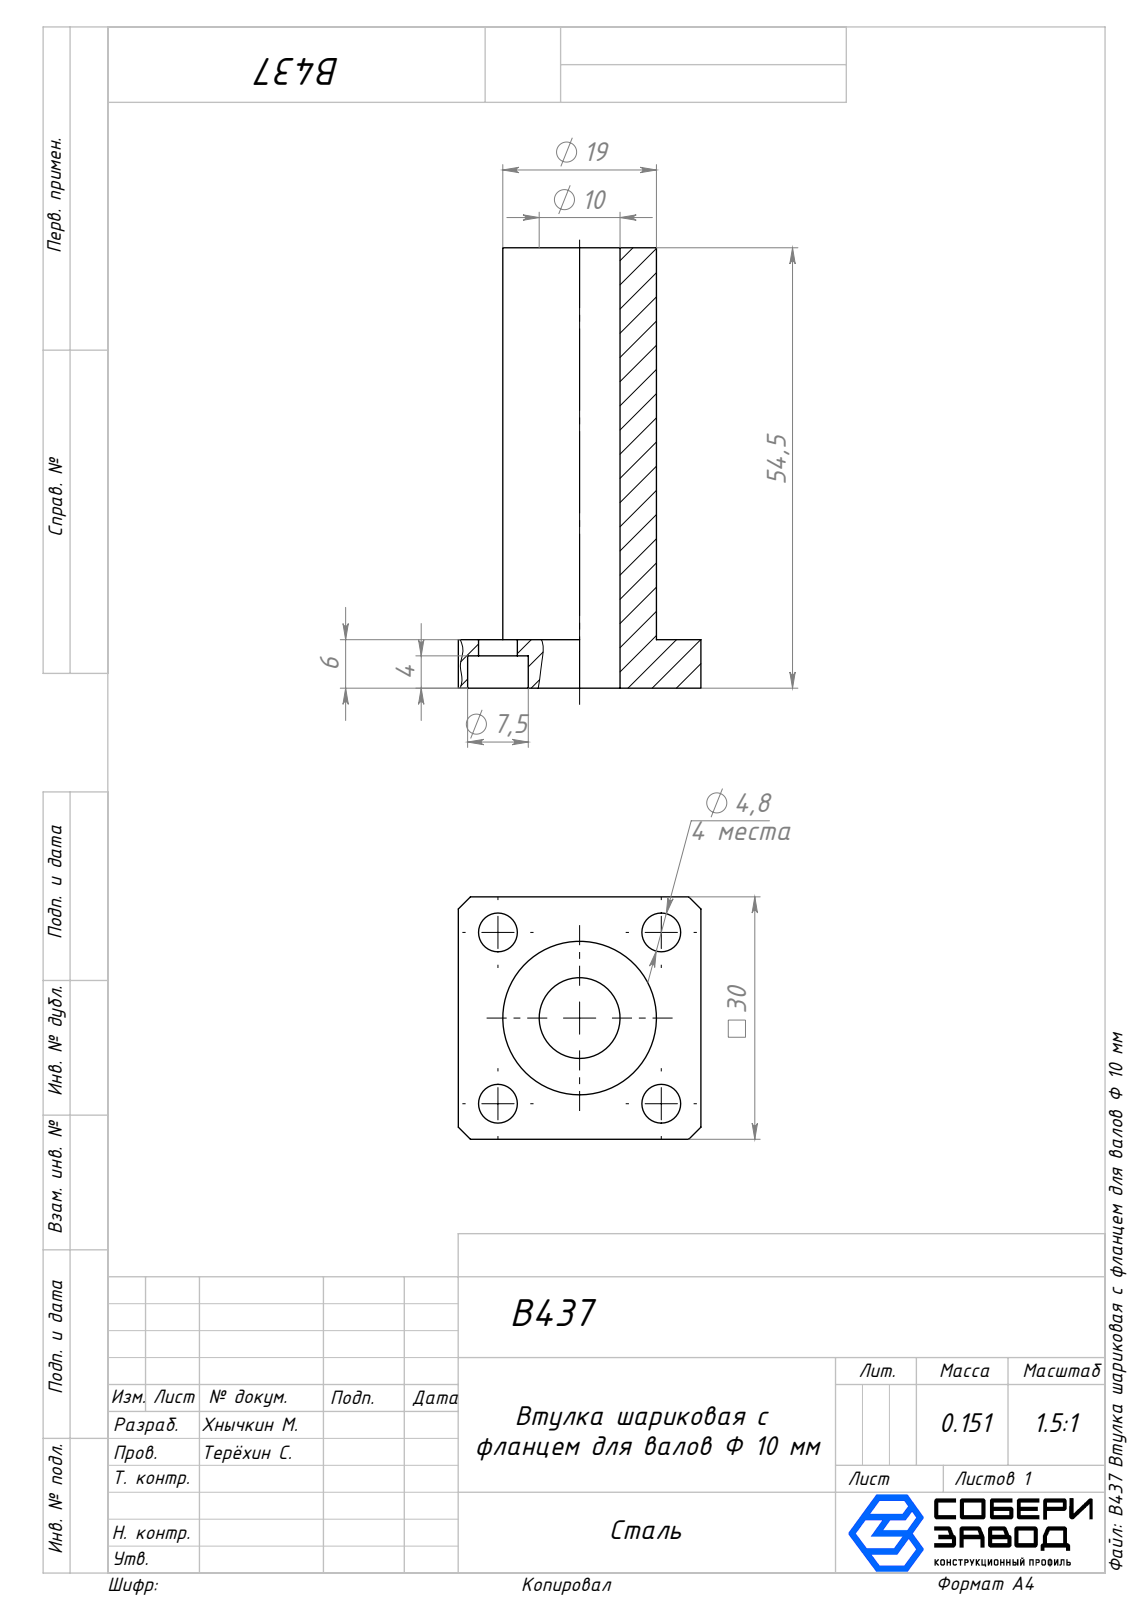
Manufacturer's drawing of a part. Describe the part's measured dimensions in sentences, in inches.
The part is named "B437 Втулка шариковая с фланцем для валов Ф 10 мм". Its 3-D file was written by "SolidWorks 2025 (AUTOMOTIVE_DESIGN)". It is 1 solid with 35 faces: 15 planar, 20 cylindrical and 0 other. Overall it measures 2.146 by 1.181 by 1.181 inches. Its volume is 0.854 cubic inches and its surface area 11.3 square inches. Round holes: 4 of diameter 0.189, 4 of diameter 0.295, 1 of diameter 0.394. Round bosses or shafts: 1 of diameter 0.748. The main face-to-face distances are 0.236, 1.181, 2.146, 1.909, 0.157, 0.079, 1.988, 1.587. The hole center spacings are 0.576, 0.795, 0.835, 1.153.
